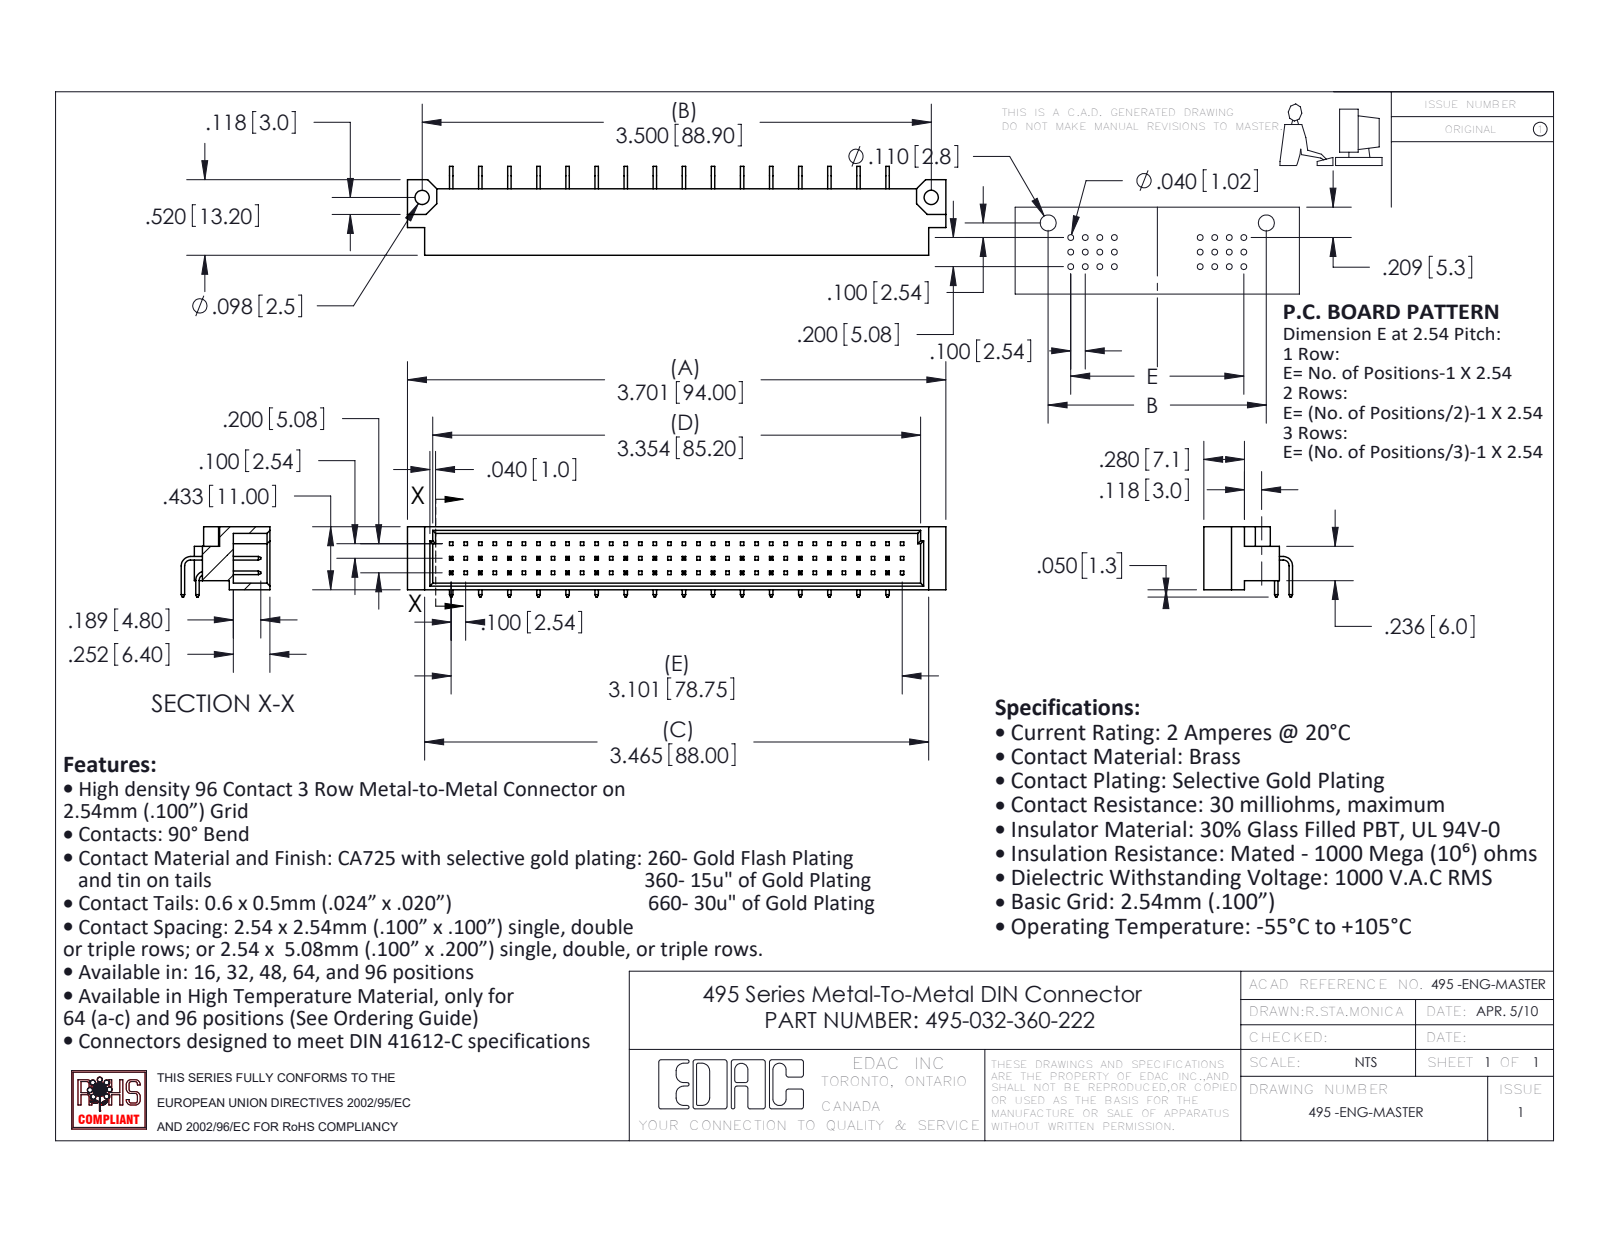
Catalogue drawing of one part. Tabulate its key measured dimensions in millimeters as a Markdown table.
| quantity | value |
| --- | --- |
| part name | 495-032-360-222; 495 Part_96; 495-290-3; 495-290-2 |
| STEP written by | SolidWorks 2020 (AUTOMOTIVE_DESIGN) |
| units | millimeters |
| bodies | 33 solids, 1009 faces (941 planar, 68 cylindrical, 0 other) |
| overall size | 94 × 15.51 × 12.27 |
| volume | 6 130 mm³ |
| surface area | 8 180 mm² |
| round holes (diameter × count) | 2.49 × 2 |
| partial cylindrical surfaces (radius × count) | 1.02 × 2, 1.65 × 2 |
| main face-to-face distances | 1.14, 9.86, 5.2, 11, 2.54, 0.61, 5.08, 8.72, 1.6, 9.4 |
| hole center spacings | 88.9 |
